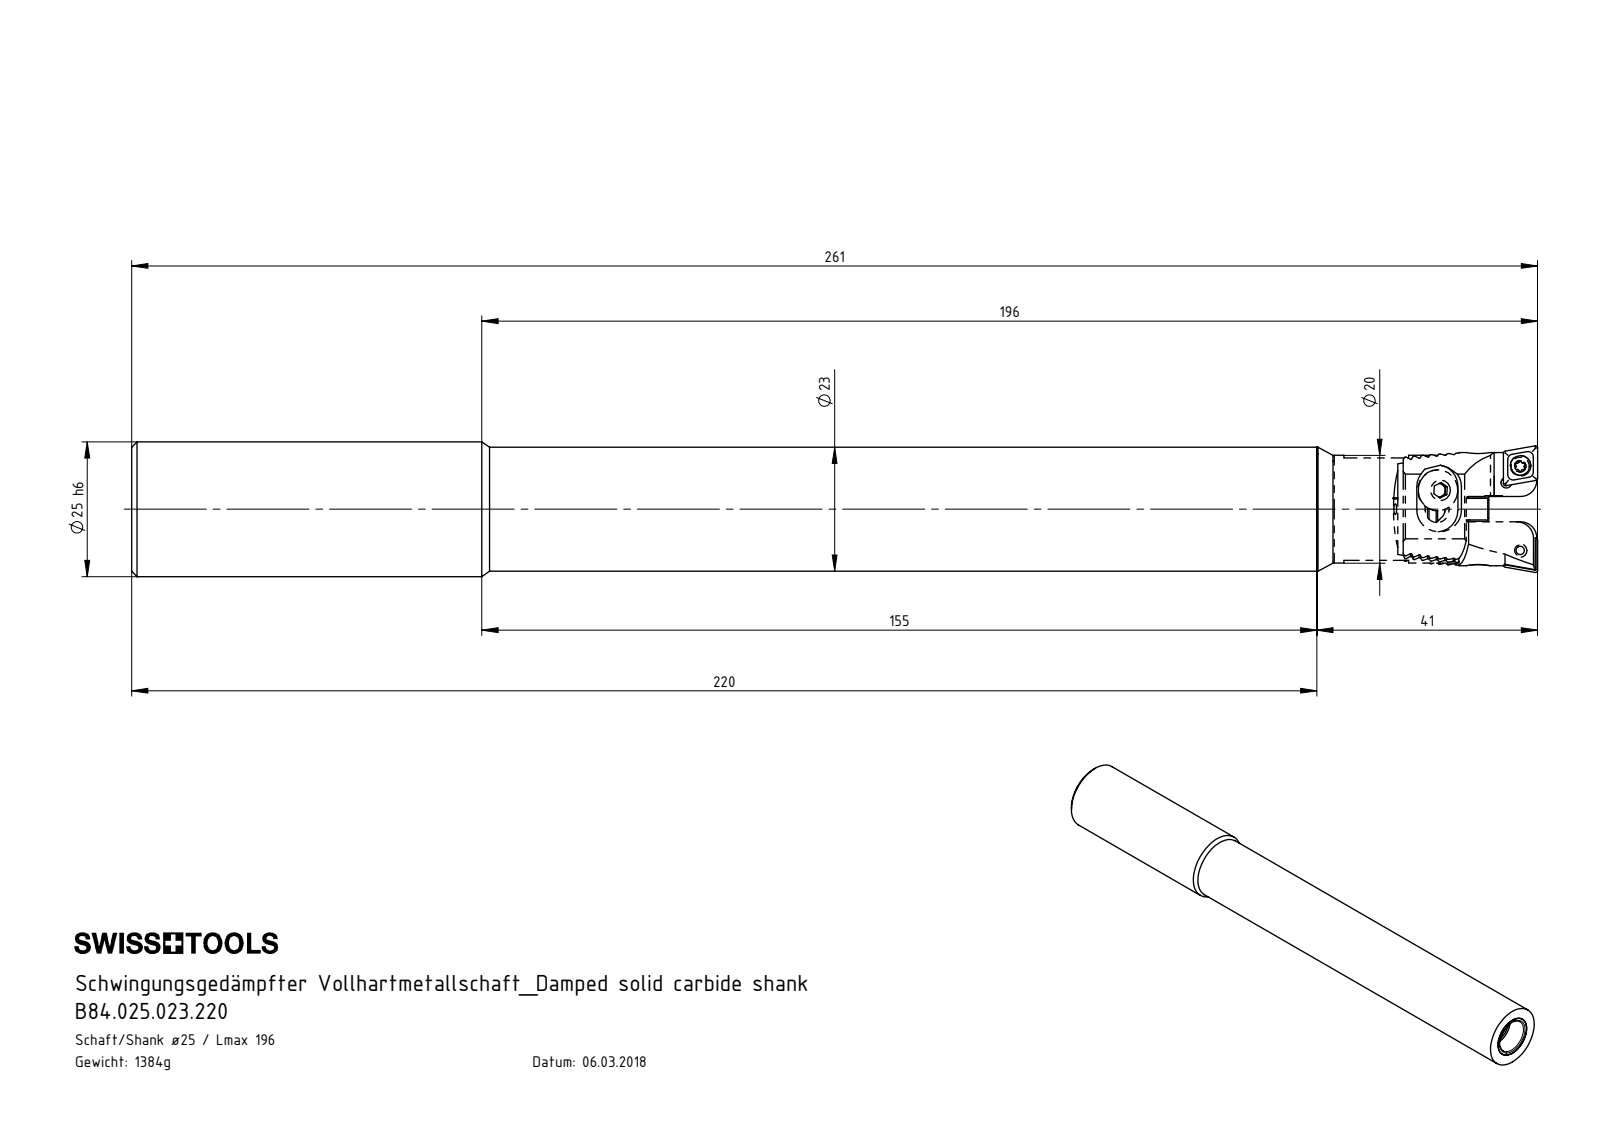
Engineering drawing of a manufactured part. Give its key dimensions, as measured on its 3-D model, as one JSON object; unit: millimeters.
{"part_name": "Z20-ER2.001.013_A; Z20-ER1.002.008_A_PreviewCfg; Z20-WCA.001.015; Z20-ER3.001.007_A (+8 more)", "step_written_by": "SolidWorks 2017 (CONFIG_CONTROL_DESIGN)", "units": "millimeters", "bodies": {"solids": 16, "faces": 808, "planar": 346, "cylindrical": 245, "other": 217}, "overall_size": [260.96, 25, 25], "volume_mm3": 102230, "surface_area_mm2": 33704, "round_holes": [[2, 6], [3.3, 3], [1, 2], [2.05, 2], [2.8, 2], [3.85, 2], [5, 2], [2.5, 1], [3.5, 1], [4.2, 1], [6.8, 1], [8.5, 1]], "round_bosses_or_shafts": [[4, 4], [7.6, 2], [3.4, 2], [2.5, 2], [25, 1], [23, 1], [20, 1], [12, 1]], "partial_cylinders_radius": [[0.12, 26], [0.21, 12], [0.36, 10], [1, 8], [0.5, 4], [2.3, 4], [4, 4], [0.36, 2]], "face_to_face_distances": [1.43, 2.86, 220, 4.29, 3, 223, 5.72, 7.15, 185, 35], "hole_center_spacings": [3.99, 4.09, 6, 13.08, 13.17, 15.96, 9.77, 11.6]}
